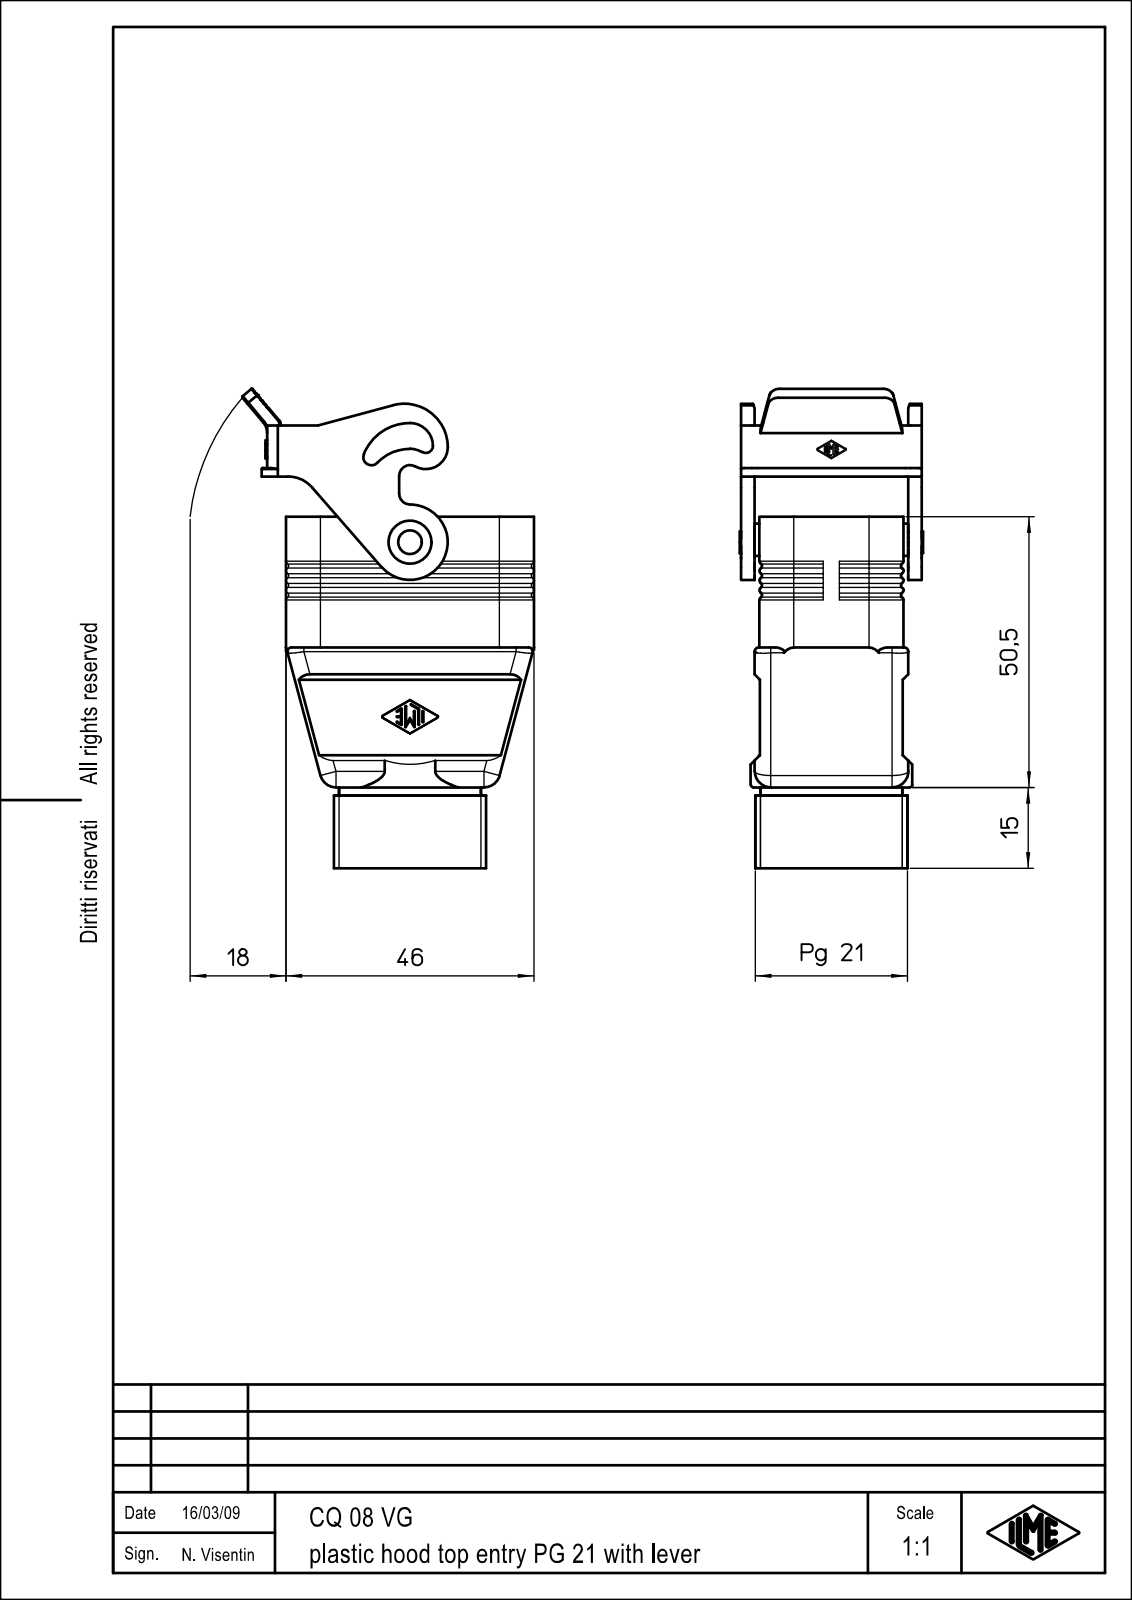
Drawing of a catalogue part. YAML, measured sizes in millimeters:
part_name: "CUSTODIA_CQ_08_V; LEVA_CQ_08_IAP; CQ_08_VG"
step_written_by: "CoCreate Modeling 16.00A 16-Aug-2008 (C) Parametric Technology GmbH (AUTOMOTIVE_DESIGN)"
units: millimeters
bodies: {solids: 2, faces: 635, planar: 251, cylindrical: 250, other: 134}
overall_size: [77.8, 63.2, 34]
volume: 26881
surface_area: 22123
round_holes:
  - {diameter: 2.4, count: 4}
  - {diameter: 4.4, count: 1}
  - {diameter: 8, count: 1}
  - {diameter: 20, count: 1}
round_bosses_or_shafts:
  - {diameter: 29, count: 1}
  - {diameter: 26.31, count: 1}
  - {diameter: 4, count: 1}
partial_cylinders:
  - {radius: 0.5, count: 36}
  - {radius: 0.1, count: 14}
  - {radius: 0.2, count: 13}
  - {radius: 3, count: 11}
  - {radius: 2, count: 5}
  - {radius: 4.5, count: 4}
  - {radius: 6.4, count: 4}
  - {radius: 1, count: 3}
face_to_face_distances: [2.75, 25.75, 2.5, 23, 3.5, 27.5, 1, 1.75, 30, 24.75]
hole_center_spacings: [17.44, 13.4, 32.2, 34.88]
